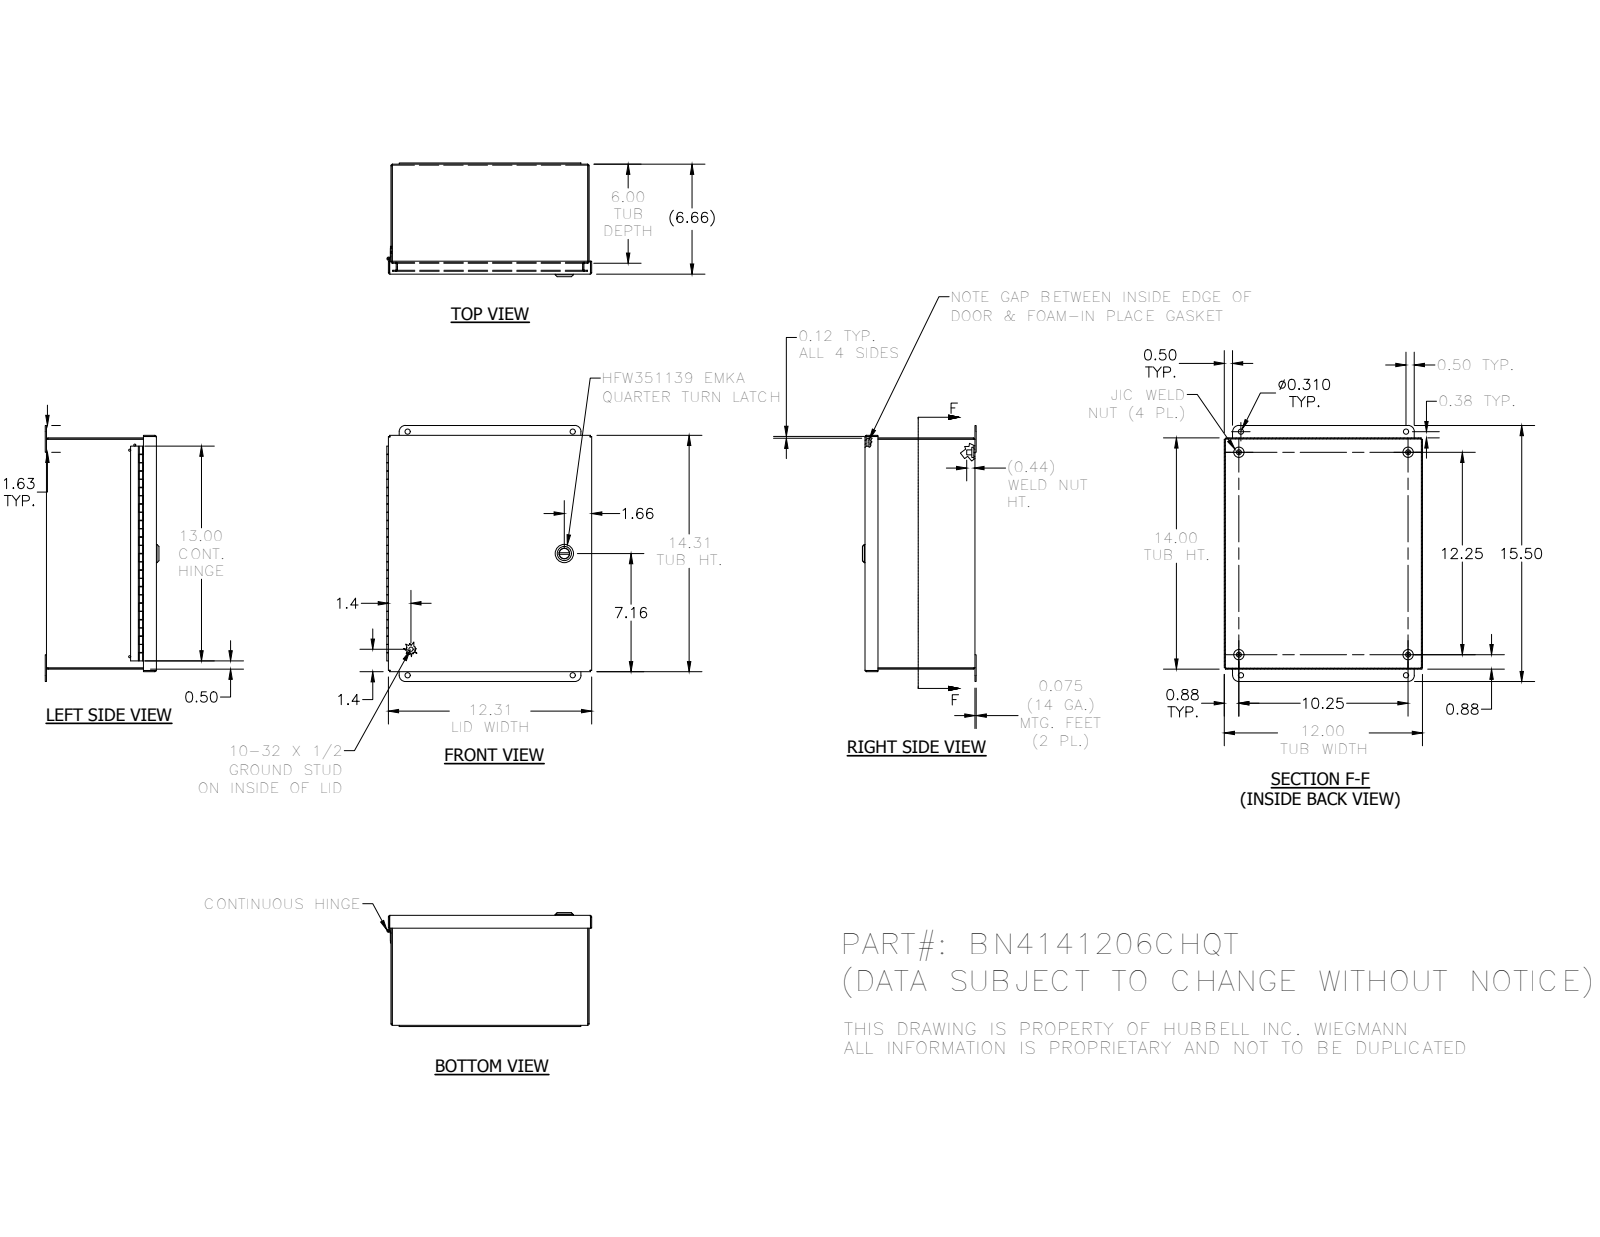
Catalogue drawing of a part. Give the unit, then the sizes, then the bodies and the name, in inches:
Units: inches
Overall size (bounding box): 15.5 × 12.406 × 6.888
Round holes (diameter × count): ⌀0.156 ×4, ⌀0.31 ×4, ⌀0.12 ×3, ⌀0.116 ×1, ⌀0.197 ×1, ⌀0.315 ×1, ⌀0.394 ×1, ⌀0.402 ×1, ⌀0.634 ×1, ⌀0.802 ×1
Round bosses / shafts (diameter × count): ⌀0.3 ×4, ⌀0.625 ×3, ⌀1.102 ×1, ⌀0.866 ×1, ⌀0.78 ×1, ⌀0.625 ×1, ⌀0.622 ×1, ⌀0.598 ×1
Partial cylindrical surfaces — rounded edges, fillets, slot ends (radius × count): R0.012 ×30, R0.031 ×20, R0.093 ×20, R0.125 ×16, R0.02 ×12, R0.157 ×4, R0.375 ×4, R0.016 ×2
Main face-to-face distances: 0.062, 0.062, 6.594, 6.656, 6.532, 6.594, 13.938, 11.938, 11.876, 12
Hole centre spacings: 16.875, 1.256, 10, 10.202, 10.202, 10.25, 12.25, 13.5
Volume: 54.77 in³ · Surface area: 1 680 in²
Bodies: 21 solids, 805 faces (408 planar, 269 cylindrical, 128 other)
Part name (STEP PRODUCT): BN4141206CHQT
STEP written by: SolidWorks 2018 (AUTOMOTIVE_DESIGN)
